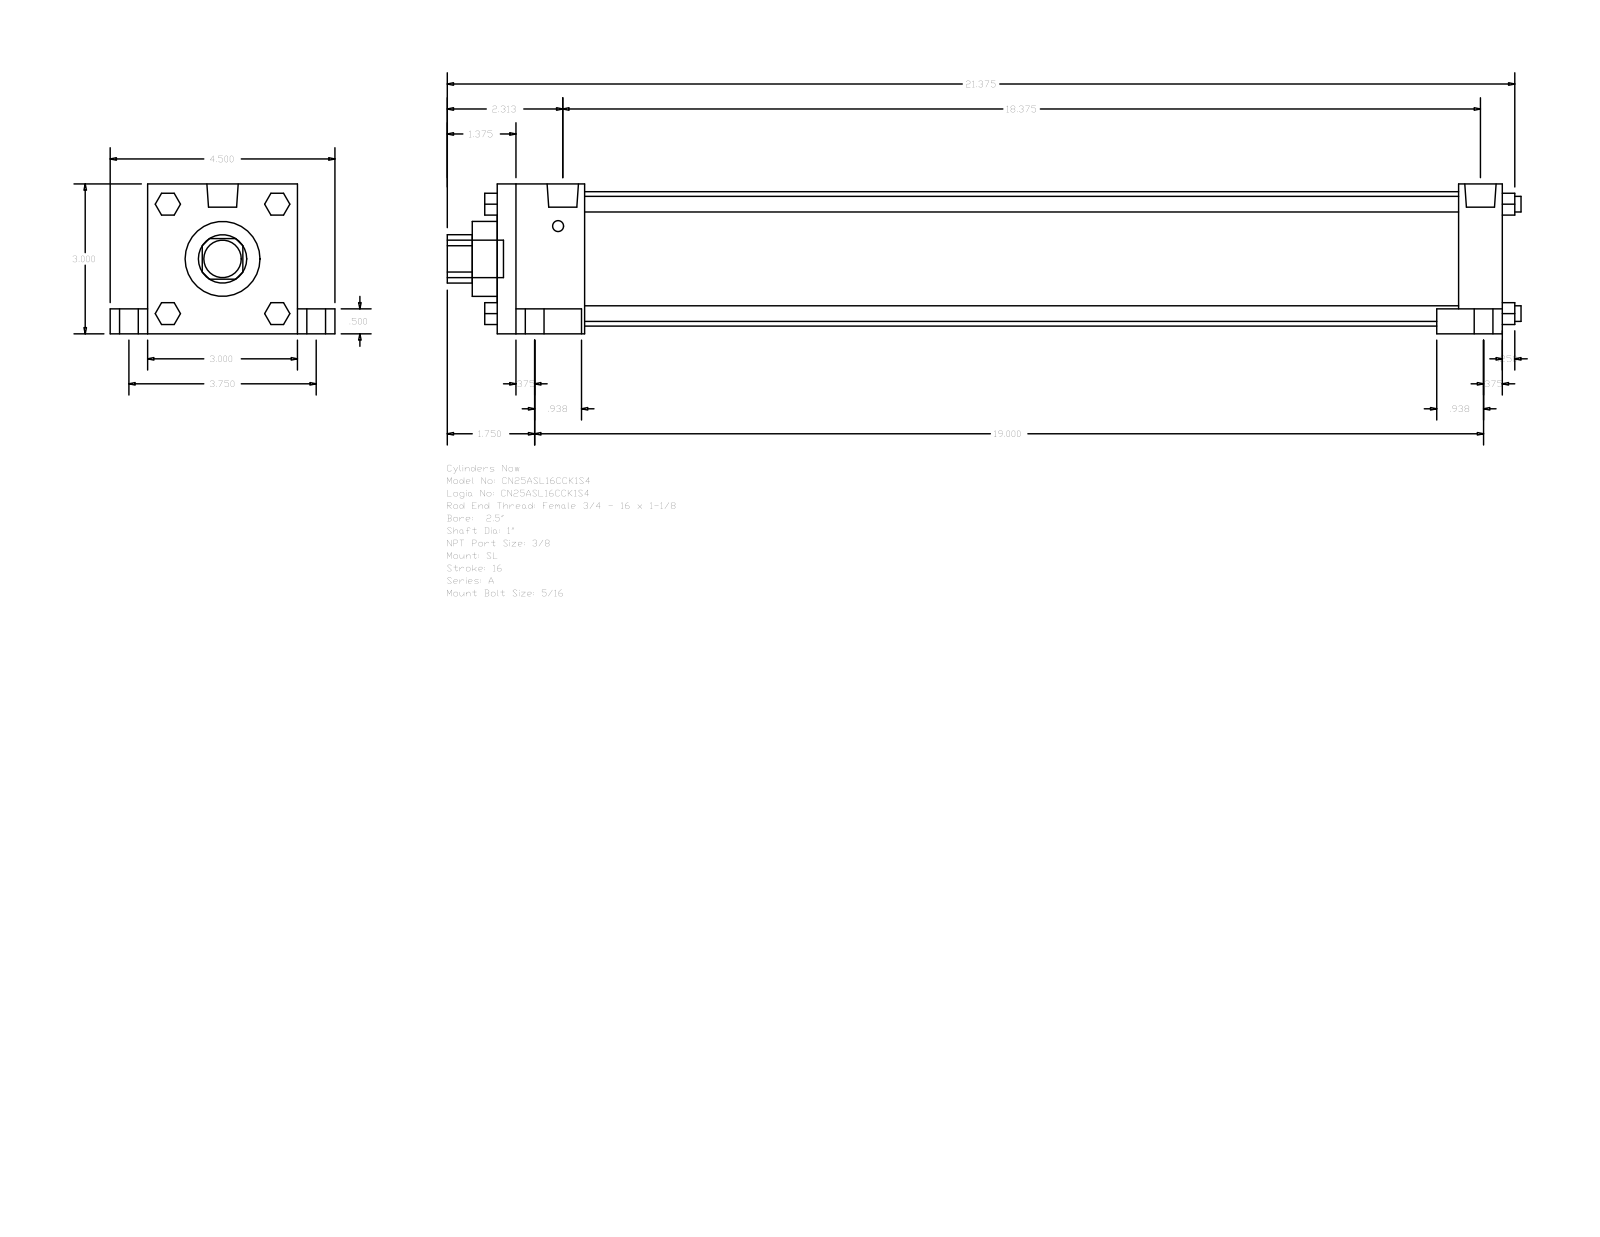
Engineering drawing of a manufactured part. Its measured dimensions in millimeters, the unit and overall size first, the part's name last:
Units: millimetres
Overall size (bounding box): 546.1 × 114.3 × 76.2
Round holes (diameter × count): ⌀25.4 ×1, ⌀38.1 ×1, ⌀68.33 ×1
Round bosses / shafts (diameter × count): ⌀15.88 ×4, ⌀9.53 ×4, ⌀7.94 ×4, ⌀5.56 ×4, ⌀15.93 ×2, ⌀19.05 ×1
Partial cylindrical surfaces — rounded edges, fillets, slot ends (radius × count): R12.29 ×1
Main face-to-face distances: 76.2, 511.18, 12.7, 44.45, 466.73, 488.95, 444.5, 22.23, 19.05, 63.5
Bodies: 0 solids, 148 faces (112 planar, 36 cylindrical, 0 other)
Part name (STEP PRODUCT): A_SL__0250_1
STEP written by: GSSL Pune (CONFIG_CONTROL_DESIGN)
